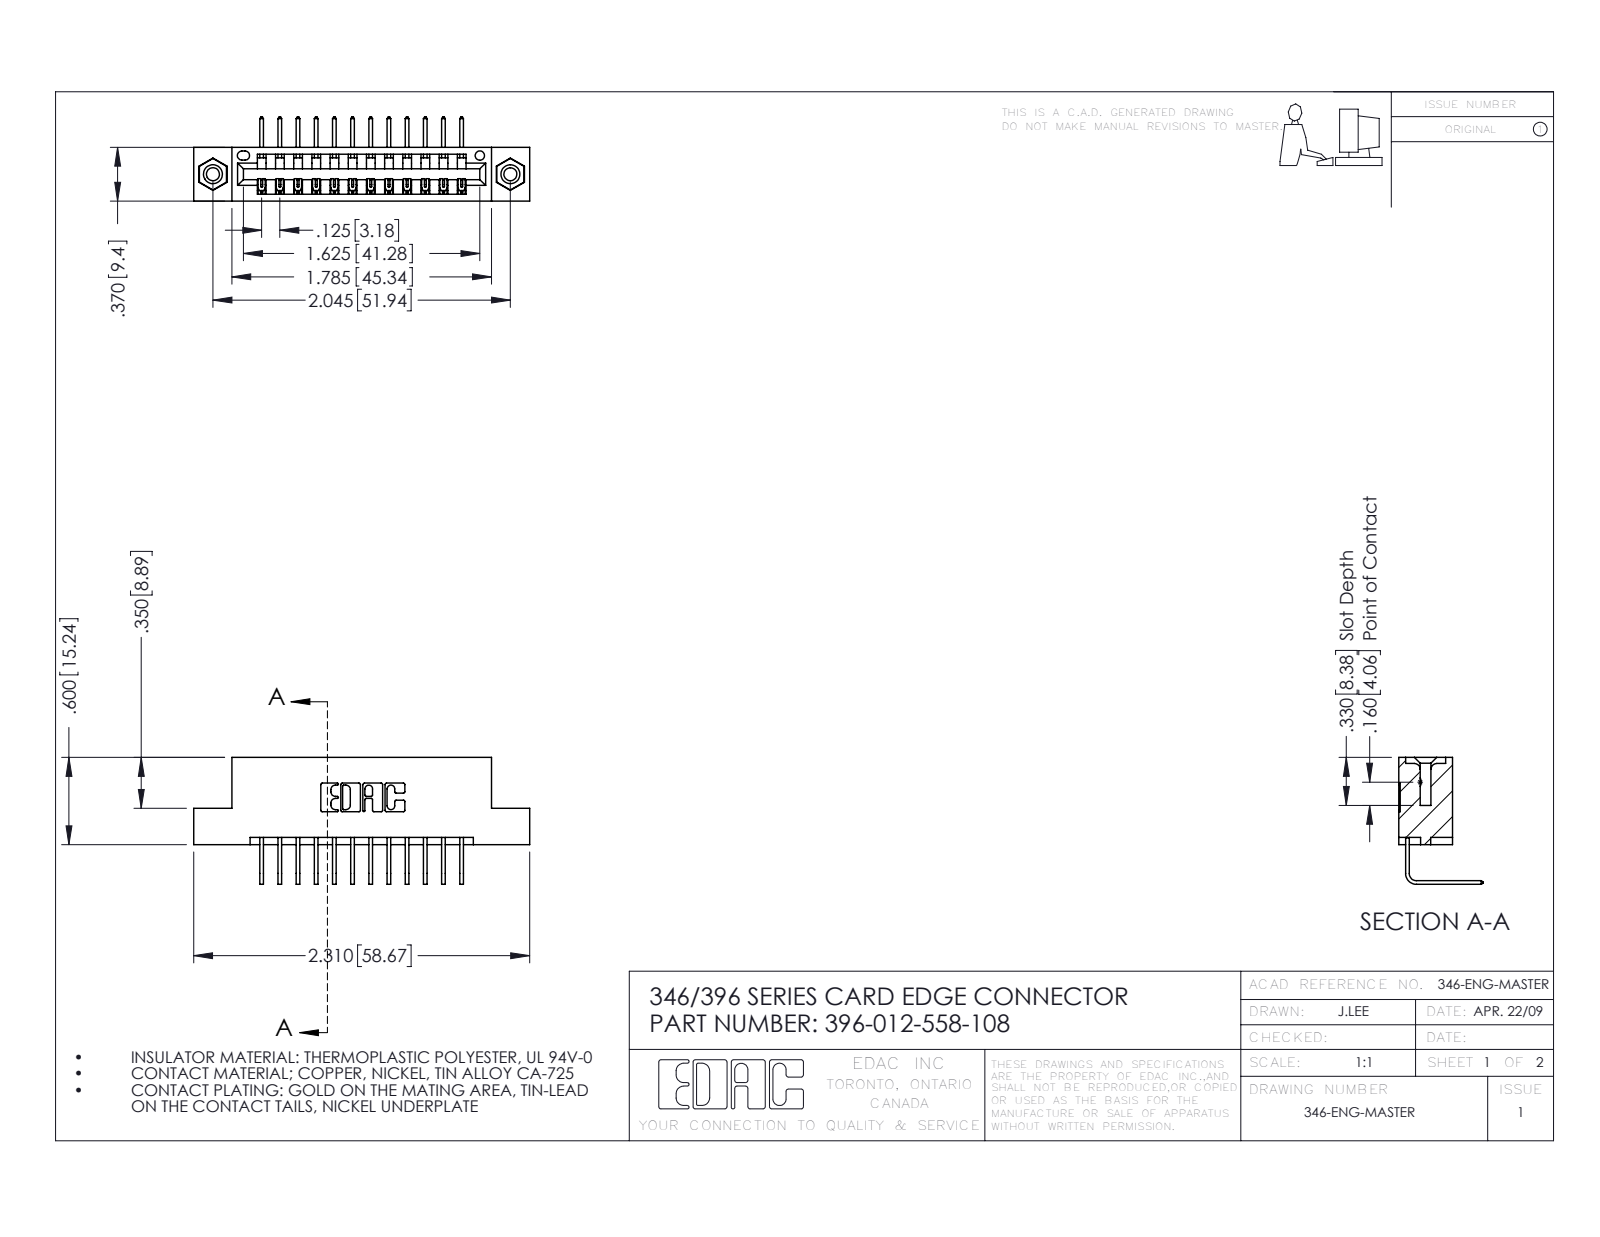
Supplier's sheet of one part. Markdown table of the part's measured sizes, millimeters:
| quantity | value |
| --- | --- |
| part name | 345-250-001_345-250-003-102; 346 Part_Flush Mounting Lugs - 0.156 Dia-TI; 396-012-558-108; 345-292-001_558 Tail - 2 |
| STEP written by | SolidWorks 2016 (CONFIG_CONTROL_DESIGN) |
| units | millimeters |
| bodies | 15 solids, 902 faces (612 planar, 274 cylindrical, 16 other) |
| overall size | 58.7 × 22.2 × 14.7 |
| volume | 5 440 mm³ |
| surface area | 6 742 mm² |
| round holes (diameter × count) | 2.3 × 2, 3.2 × 2, 4 × 2, 1.6 × 1 |
| round bosses / shafts (diameter × count) | 3.9 × 2 |
| partial cylindrical surfaces (radius × count) | 0.2 × 24, 0.3 × 22, 0.2 × 6, 0.8 × 6, 0.7 × 3, 0.8 × 2, 1 × 2, 0.4 × 1 |
| main face-to-face distances | 6.4, 8.2, 1.2, 9.4, 7.6, 0.6, 1.8, 3.8, 5.6, 2.5 |
| hole center spacings | 6.2, 46.7, 51.9 |
